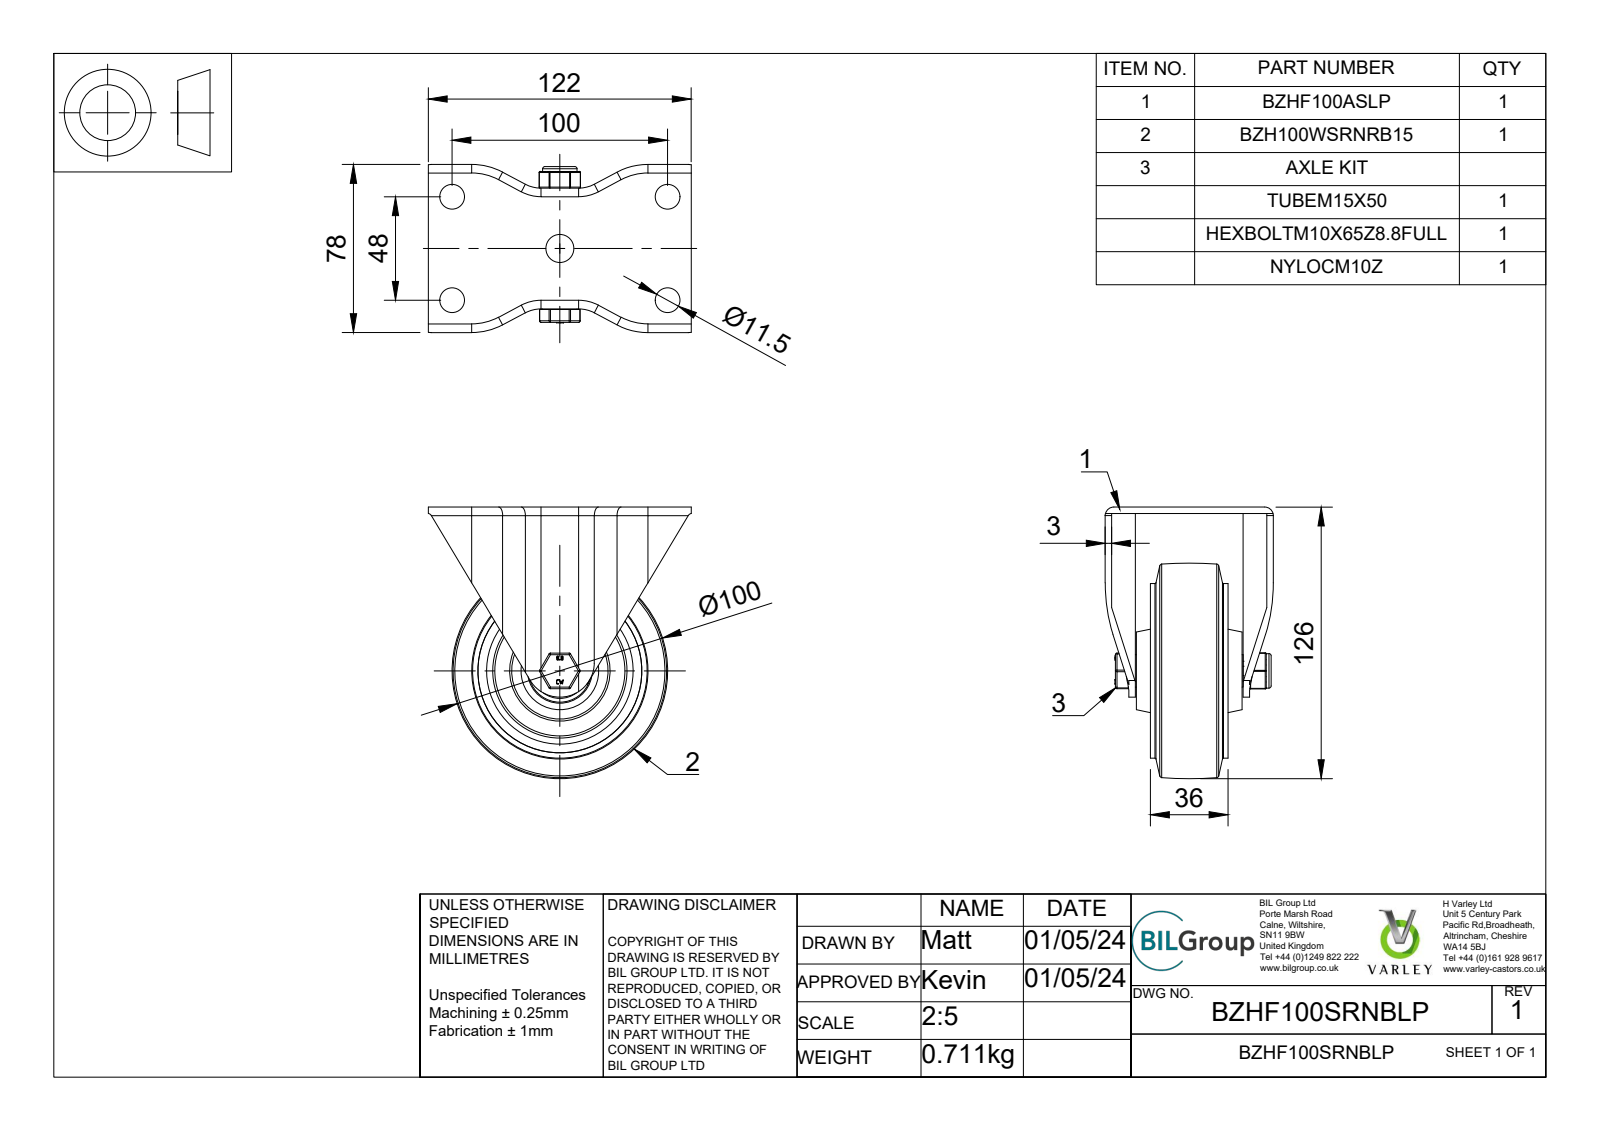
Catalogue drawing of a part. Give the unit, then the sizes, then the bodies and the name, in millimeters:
Units: millimetres
Overall size (bounding box): 126 × 122 × 78
Round holes (diameter × count): ⌀11.5 ×4, ⌀10 ×1, ⌀10.5 ×1, ⌀10.8 ×1, ⌀12 ×1, ⌀13 ×1, ⌀15 ×1, ⌀23 ×1, ⌀30 ×1, ⌀76 ×1
Round bosses / shafts (diameter × count): ⌀4 ×8, ⌀81 ×1, ⌀22.75 ×1, ⌀16 ×1, ⌀9.85 ×1, ⌀8.14 ×1
Partial cylindrical surfaces — rounded edges, fillets, slot ends (radius × count): R0.5 ×18, R0.75 ×12, R4 ×8, R15.5 ×4, R30.5 ×4, R2 ×2, R9.38 ×1, R16 ×1
Main face-to-face distances: 3, 21, 11, 64, 7, 46, 43, 34.66, 10, 53
Hole centre spacings: 55.46, 48, 100, 110.92
Volume: 276 452 mm³ · Surface area: 116 869 mm²
Bodies: 16 solids, 454 faces (179 planar, 189 cylindrical, 86 other)
Part name (STEP PRODUCT): BZHF100SRNBLP v3; BZHF100ASLP - 50 v1; ZINC PLATED PRESSED STEEL BRACKET; BZH100WSRNRB15 v1 (+7 more)
STEP written by: Autodesk Translation Framework v12.20.1.177 (AUTOMOTIVE_DESIGN)
